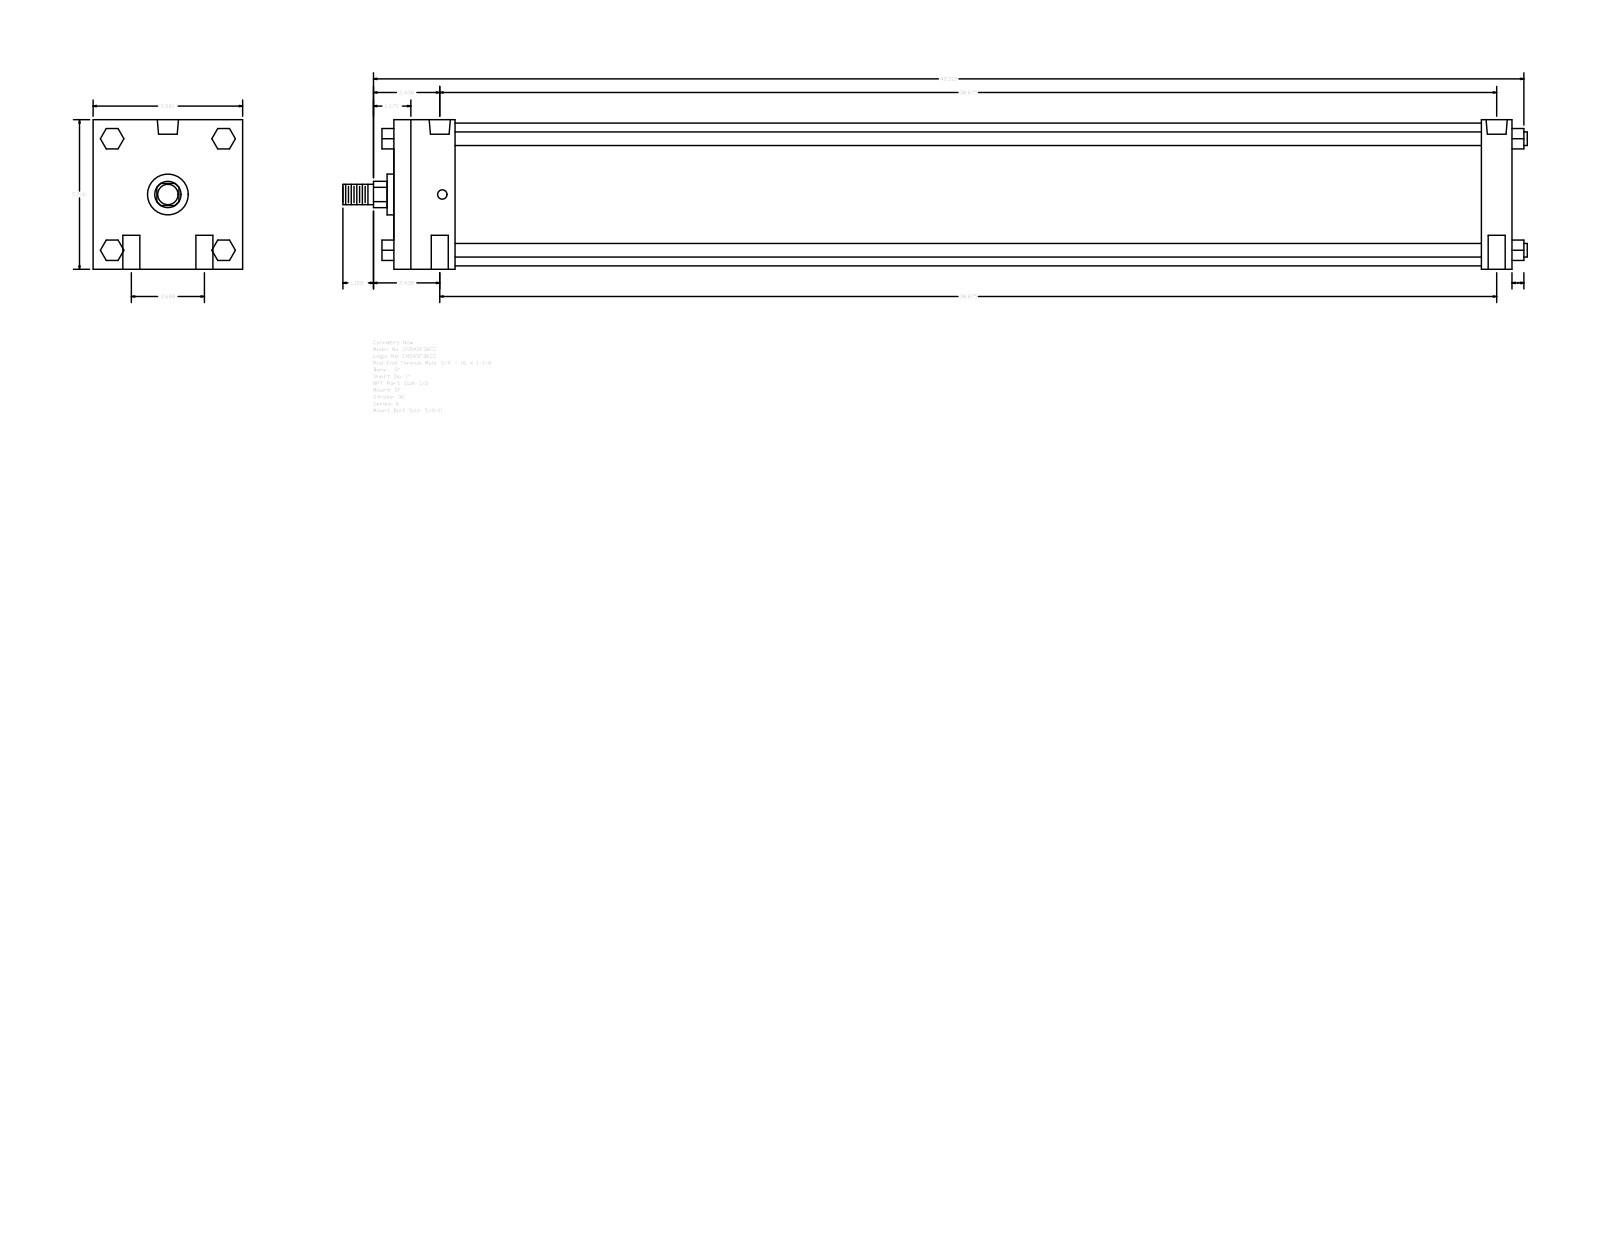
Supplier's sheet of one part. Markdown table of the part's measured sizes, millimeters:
| quantity | value |
| --- | --- |
| part name | A_SF__0500_1 |
| STEP written by | GSSL Pune (CONFIG_CONTROL_DESIGN) |
| units | millimeters |
| bodies | 0 solids, 124 faces (94 planar, 30 cylindrical, 0 other) |
| overall size | 1106.49 × 139.7 × 139.7 |
| round holes (diameter × count) | 15.88 × 4, 8.73 × 2, 19.77 × 2 |
| round bosses / shafts (diameter × count) | 12.7 × 4, 133.35 × 1, 38.1 × 1, 25.4 × 1, 19.05 × 1 |
| partial cylindrical surfaces (radius × count) | 12.29 × 1 |
| main face-to-face distances | 139.7, 1044.57, 28.57, 57.15, 1016, 958.85, 987.42, 19.05, 52.07, 90.18 |
| hole center spacings | 34.13, 988.02, 987.43, 68.26, 989.79, 982.65 |
